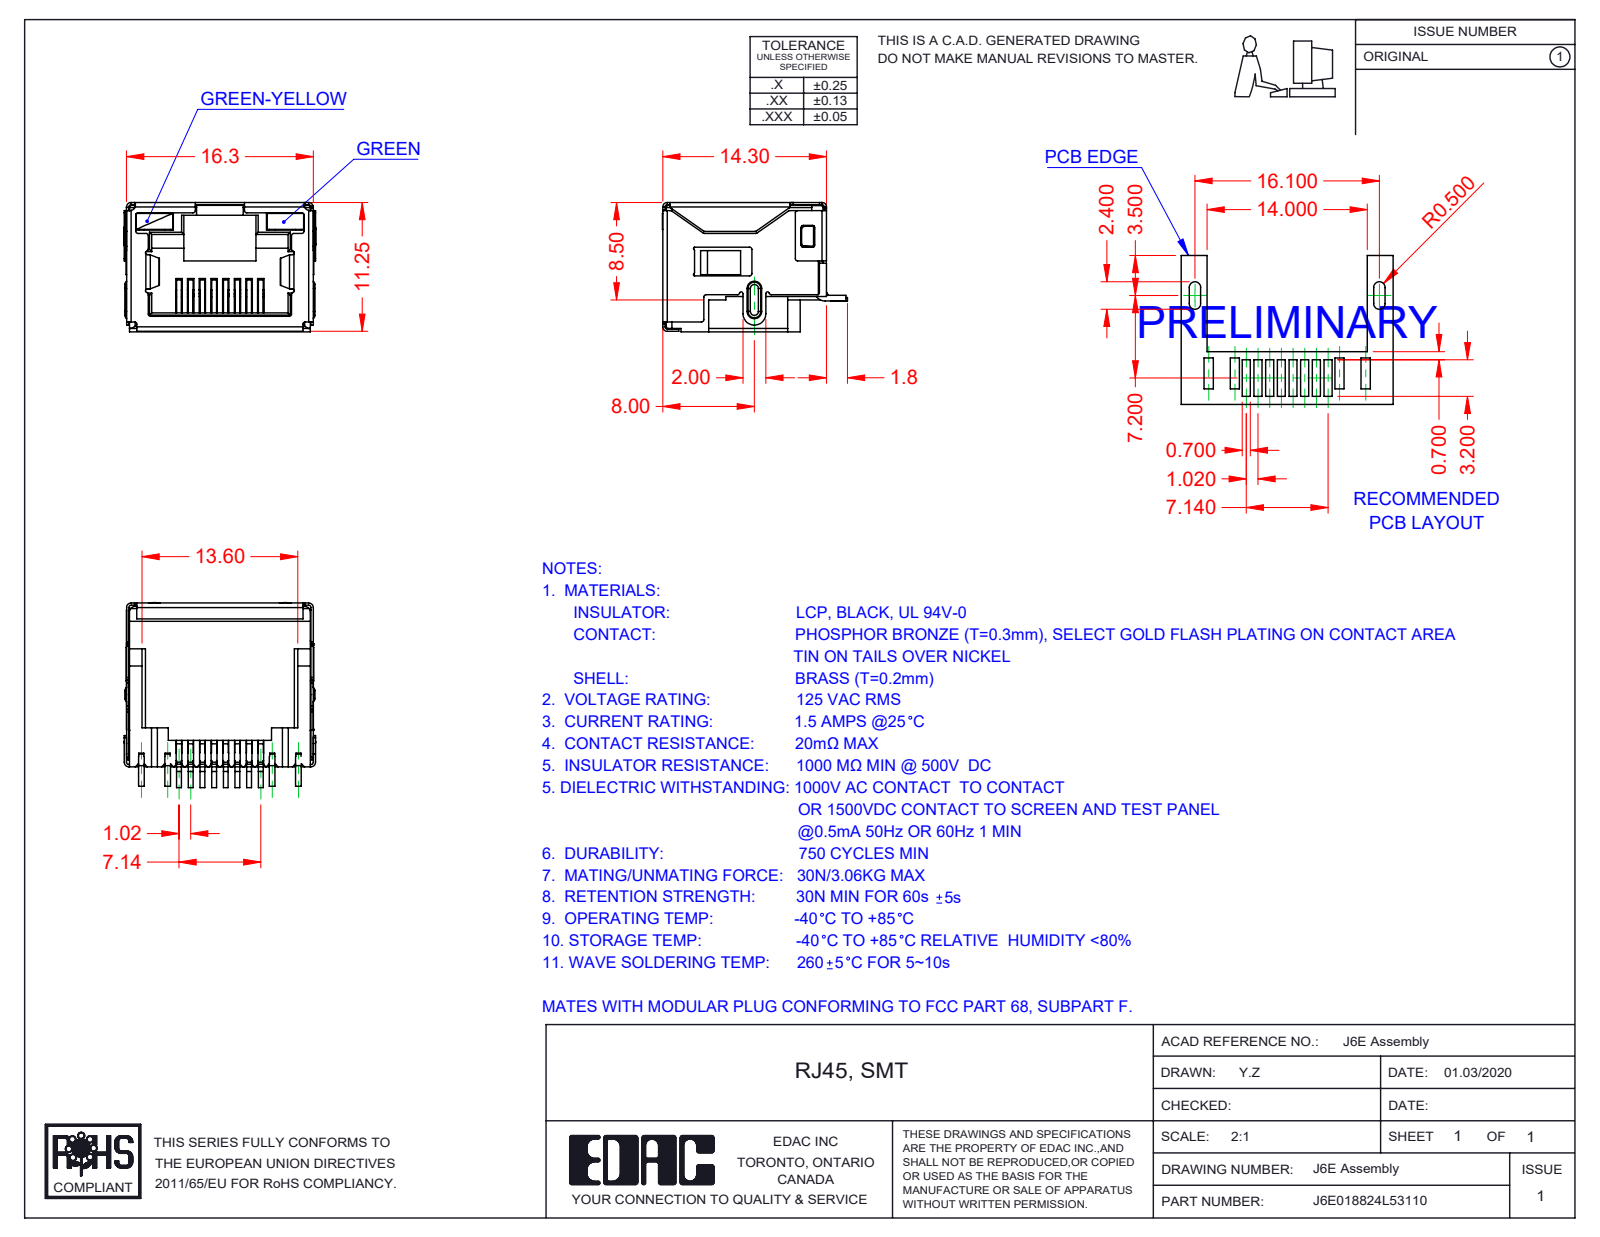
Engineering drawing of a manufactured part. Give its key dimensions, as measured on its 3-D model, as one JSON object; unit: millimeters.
{"part_name": "6E LED LH_5-Green-Yellow; J6E018824L53110; 6E Shield_LED; 6E Insulator_LED (+2 more)", "step_written_by": "SolidWorks 2016 (CONFIG_CONTROL_DESIGN)", "units": "millimeters", "bodies": {"solids": 12, "faces": 1498, "planar": 1099, "cylindrical": 349, "other": 50}, "overall_size": [16.75, 16.15, 11.3], "volume_mm3": 1109, "surface_area_mm2": 4045, "partial_cylinders_radius": [[0.2, 82], [0.25, 17], [0.4, 13], [0.5, 13], [0.1, 10], [0.15, 7], [0.3, 4], [1, 3]], "face_to_face_distances": [11.05, 16.05, 16.1, 15.85, 11.1, 11.3, 2.4, 0.7, 9.85, 0.49]}
